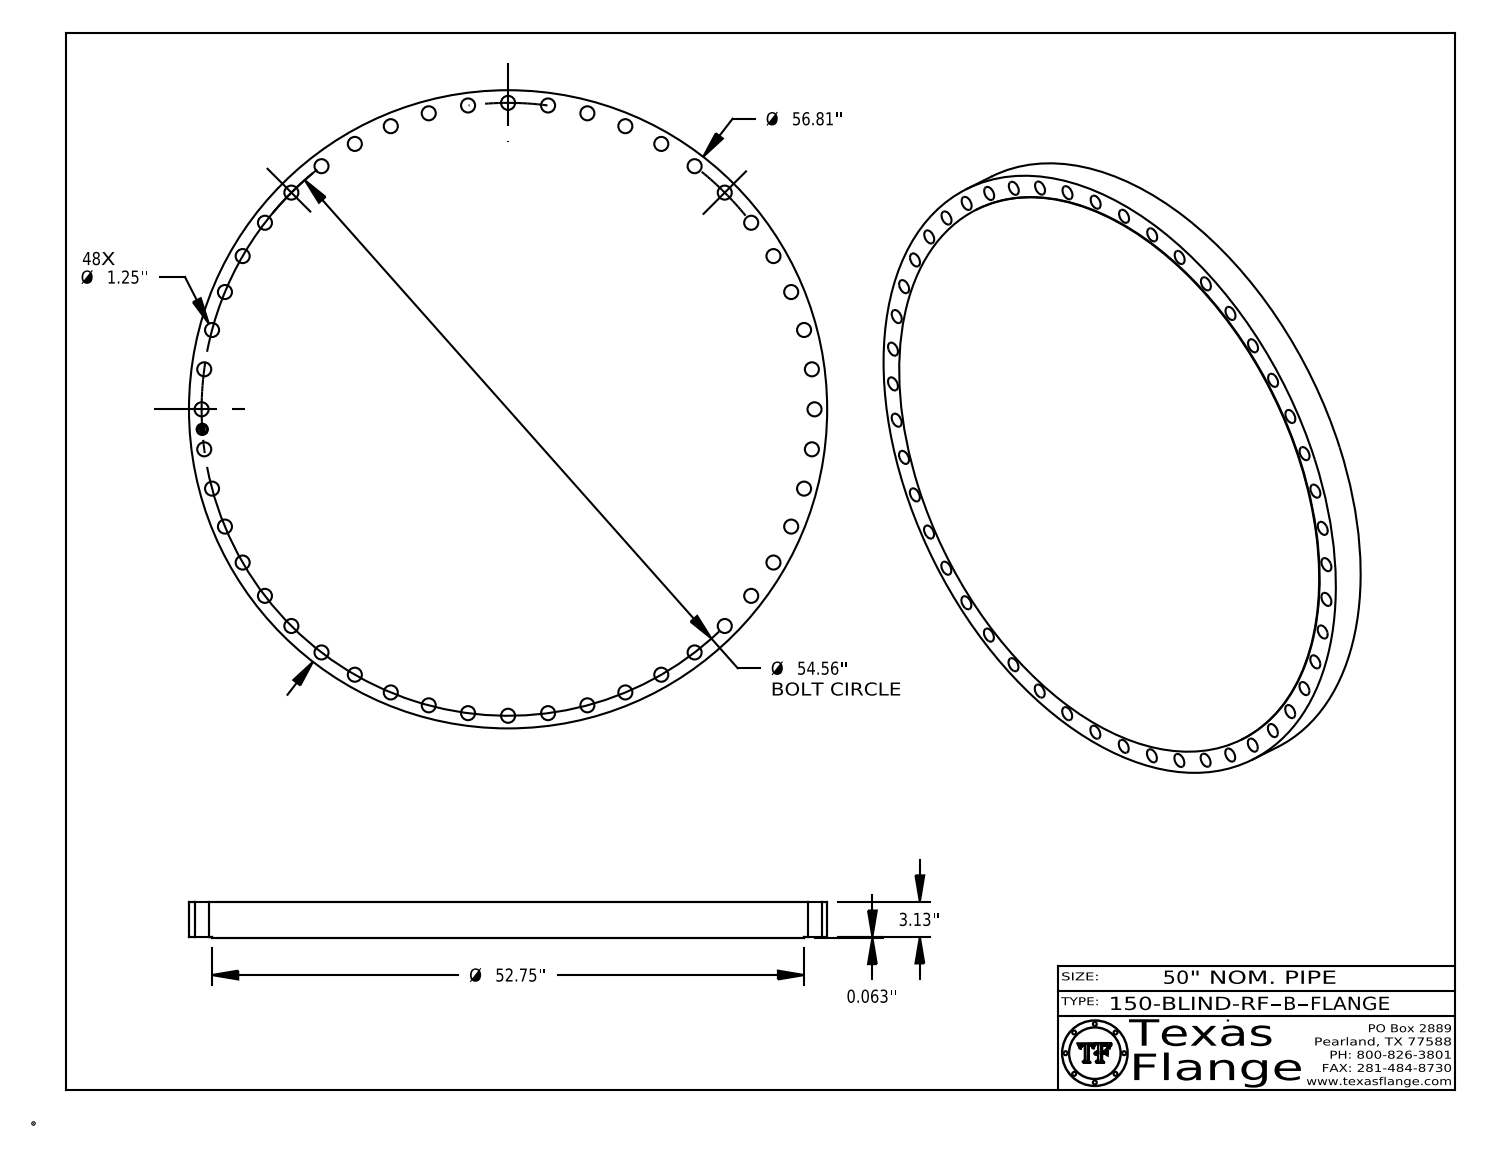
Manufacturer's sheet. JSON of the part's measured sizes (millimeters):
{"part_name": "150-BLIND-RF, Series B", "step_written_by": "CATIA V5 STEP AP214 (AUTOMOTIVE_DESIGN)", "units": "millimeters", "bodies": {"solids": 1, "faces": 488, "planar": 368, "cylindrical": 120, "other": 0}, "overall_size": [1443, 1443, 81.1], "volume_mm3": 129200000, "surface_area_mm2": 3943000, "round_holes": [[31.8, 48], [25.4, 1]], "round_bosses_or_shafts": [[1.5, 8], [1443, 1], [1339.9, 1], [20, 1]], "face_to_face_distances": [81.1, 1.6, 79.5, 80.7, 79.1, 0.4, 7.6, 7.4, 1.4, 4.9], "hole_center_spacings": [90.7, 1374, 180.9, 270.4, 445.5, 1338.6, 530.3, 1382.9]}
